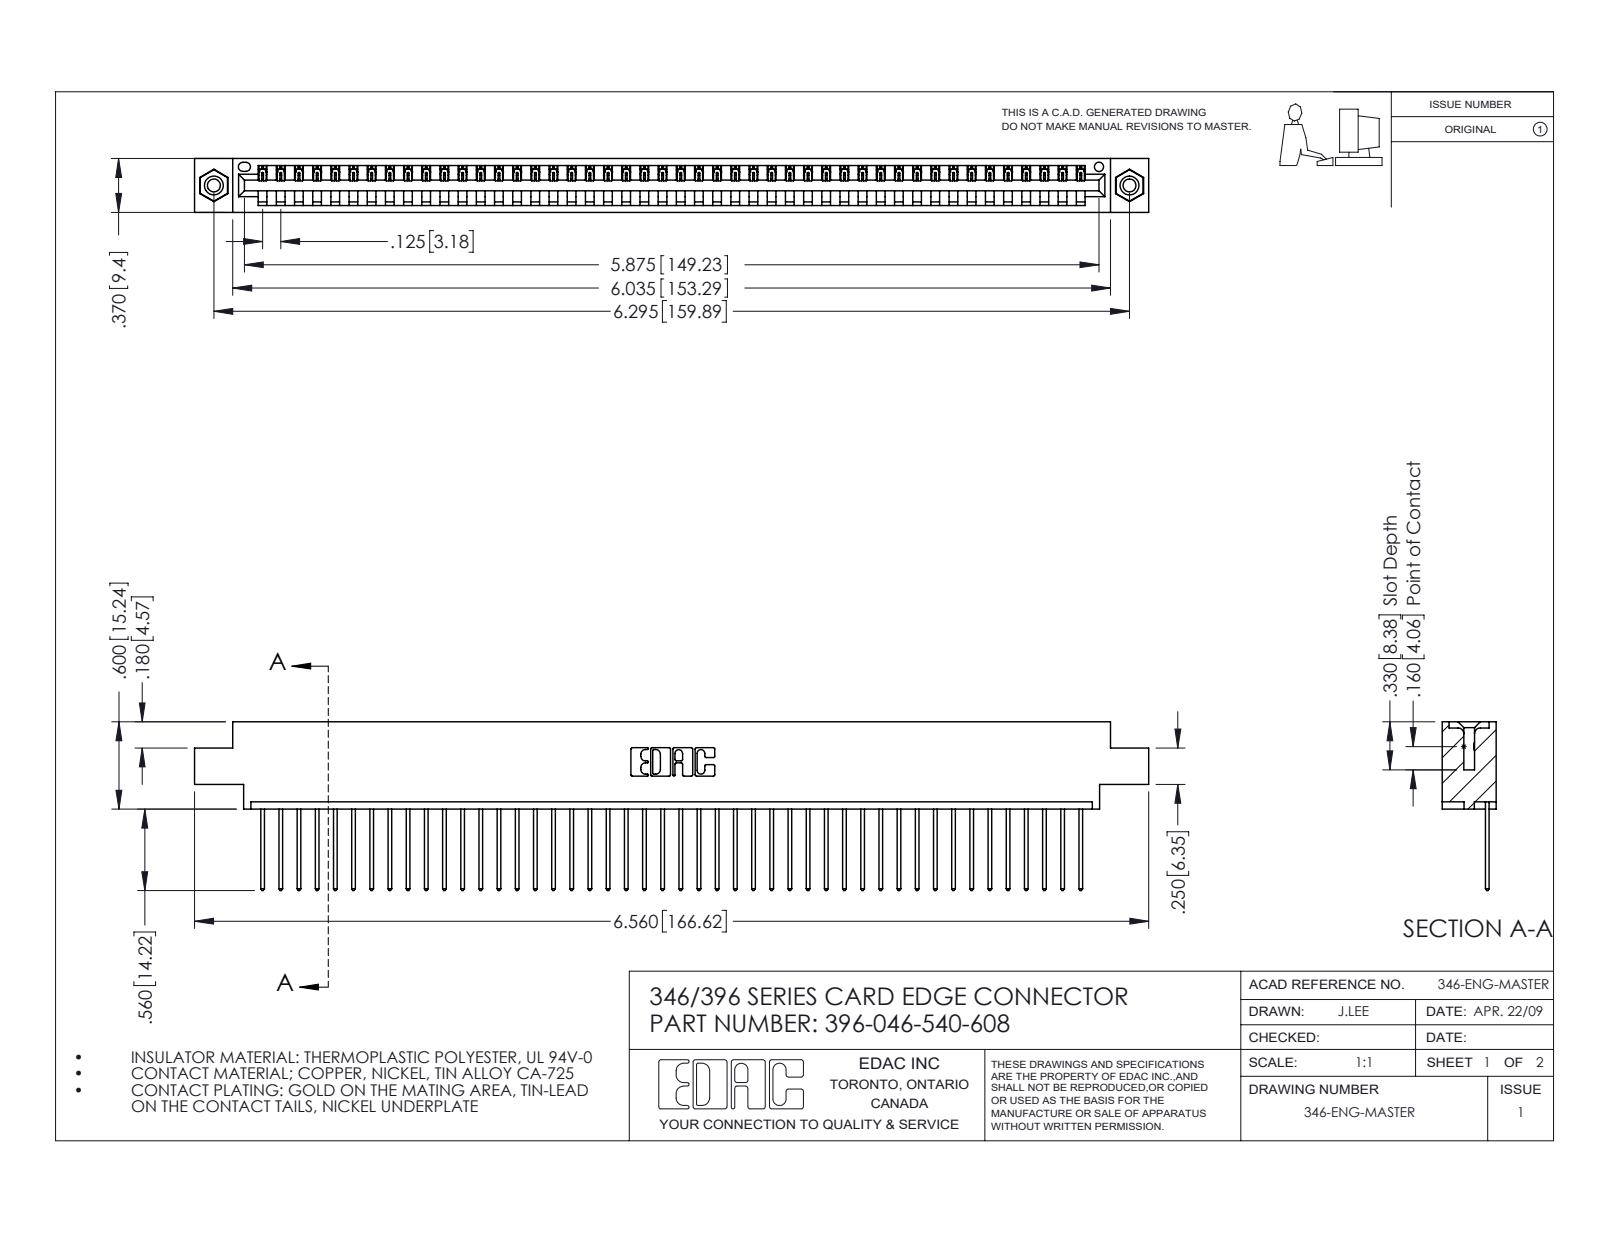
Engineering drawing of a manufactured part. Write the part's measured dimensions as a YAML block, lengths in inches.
part_name: "396-046-540-608; 346 Part_0.170 Offset - 0.156 Dia-TI; 345-292-001_345-293-140; 345-250-001_345-250-003-102"
step_written_by: "SolidWorks 2016 (CONFIG_CONTROL_DESIGN)"
units: inches
bodies: {solids: 49, faces: 2854, planar: 1952, cylindrical: 886, other: 16}
overall_size: [6.56, 1.16, 0.37]
volume: 0.969
surface_area: 31.82
round_holes:
  - {diameter: 0.089, count: 2}
  - {diameter: 0.125, count: 2}
  - {diameter: 0.156, count: 2}
  - {diameter: 0.064, count: 1}
round_bosses_or_shafts:
  - {diameter: 0.155, count: 2}
partial_cylinders:
  - {radius: 0.006, count: 92}
  - {radius: 0.01, count: 92}
  - {radius: 0.01, count: 22}
  - {radius: 0.007, count: 6}
  - {radius: 0.031, count: 6}
  - {radius: 0.026, count: 3}
  - {radius: 0.031, count: 2}
  - {radius: 0.04, count: 2}
face_to_face_distances: [0.048, 0.322, 0.37, 0.25, 0.072, 0.298, 0.025, 0.222, 0.148, 0.1]
hole_center_spacings: [0.246, 6.086, 6.295]
